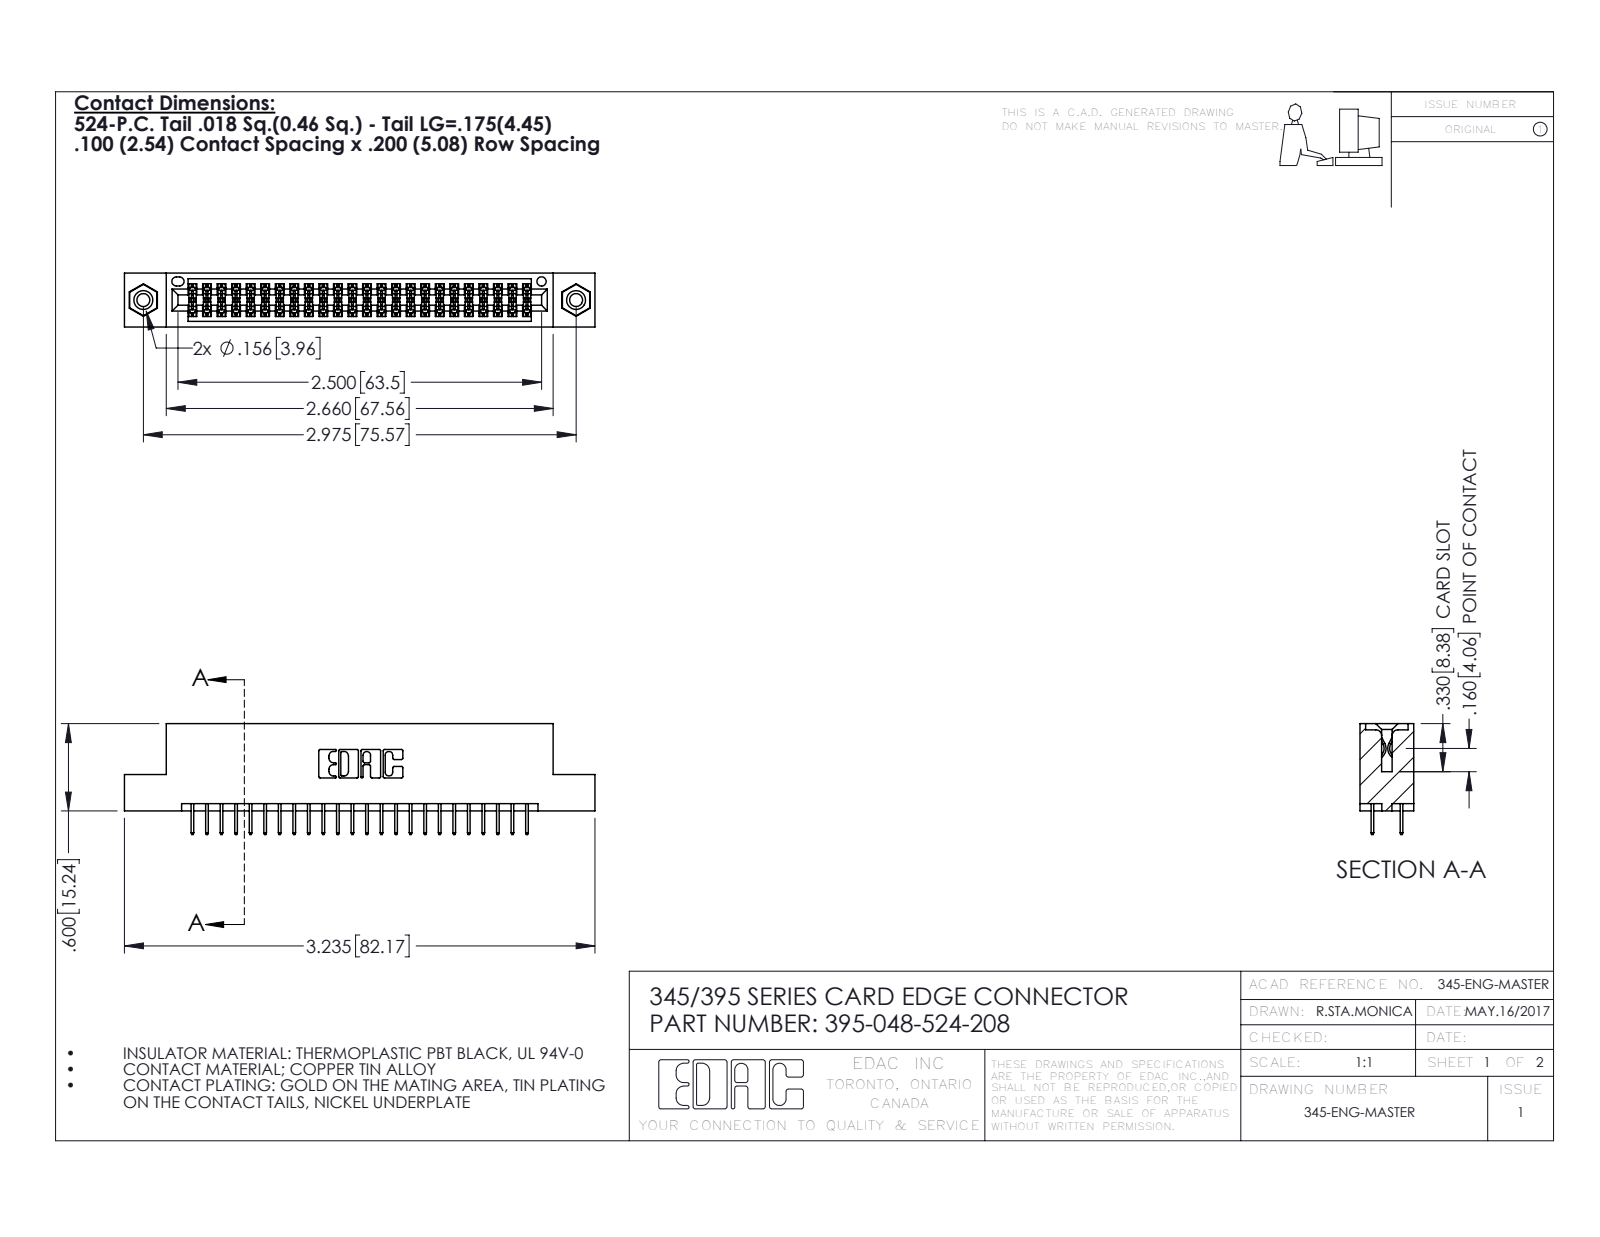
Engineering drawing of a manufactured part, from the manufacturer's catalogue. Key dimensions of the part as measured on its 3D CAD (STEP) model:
Part name (STEP PRODUCT): 345-292-001_345-293-124; 345 Part_Flush Mounting Lugs - 0.156 Dia-TI; 395-048-524-208; 345-250-001_345-250-003-102
STEP written by: SolidWorks 2016 (CONFIG_CONTROL_DESIGN)
Units: inches
Bodies: 51 solids, 2778 faces (1984 planar, 778 cylindrical, 16 other)
Overall size (bounding box): 3.235 × 0.762 × 0.37
Volume: 0.472 in³ · Surface area: 16.91 in²
Round holes (diameter × count): ⌀0.089 ×2, ⌀0.125 ×2, ⌀0.156 ×2, ⌀0.064 ×1
Round bosses / shafts (diameter × count): ⌀0.155 ×2
Partial cylindrical surfaces — rounded edges, fillets, slot ends (radius × count): R0.006 ×72, R0.01 ×22, R0.007 ×6, R0.031 ×6, R0.026 ×3, R0.014 ×2, R0.019 ×2, R0.022 ×2
Main face-to-face distances: 0.072, 0.298, 0.2, 0.37, 0.098, 0.272, 0.025, 0.225, 0.072, 0.175
Hole centre spacings: 0.27, 2.741, 2.975
